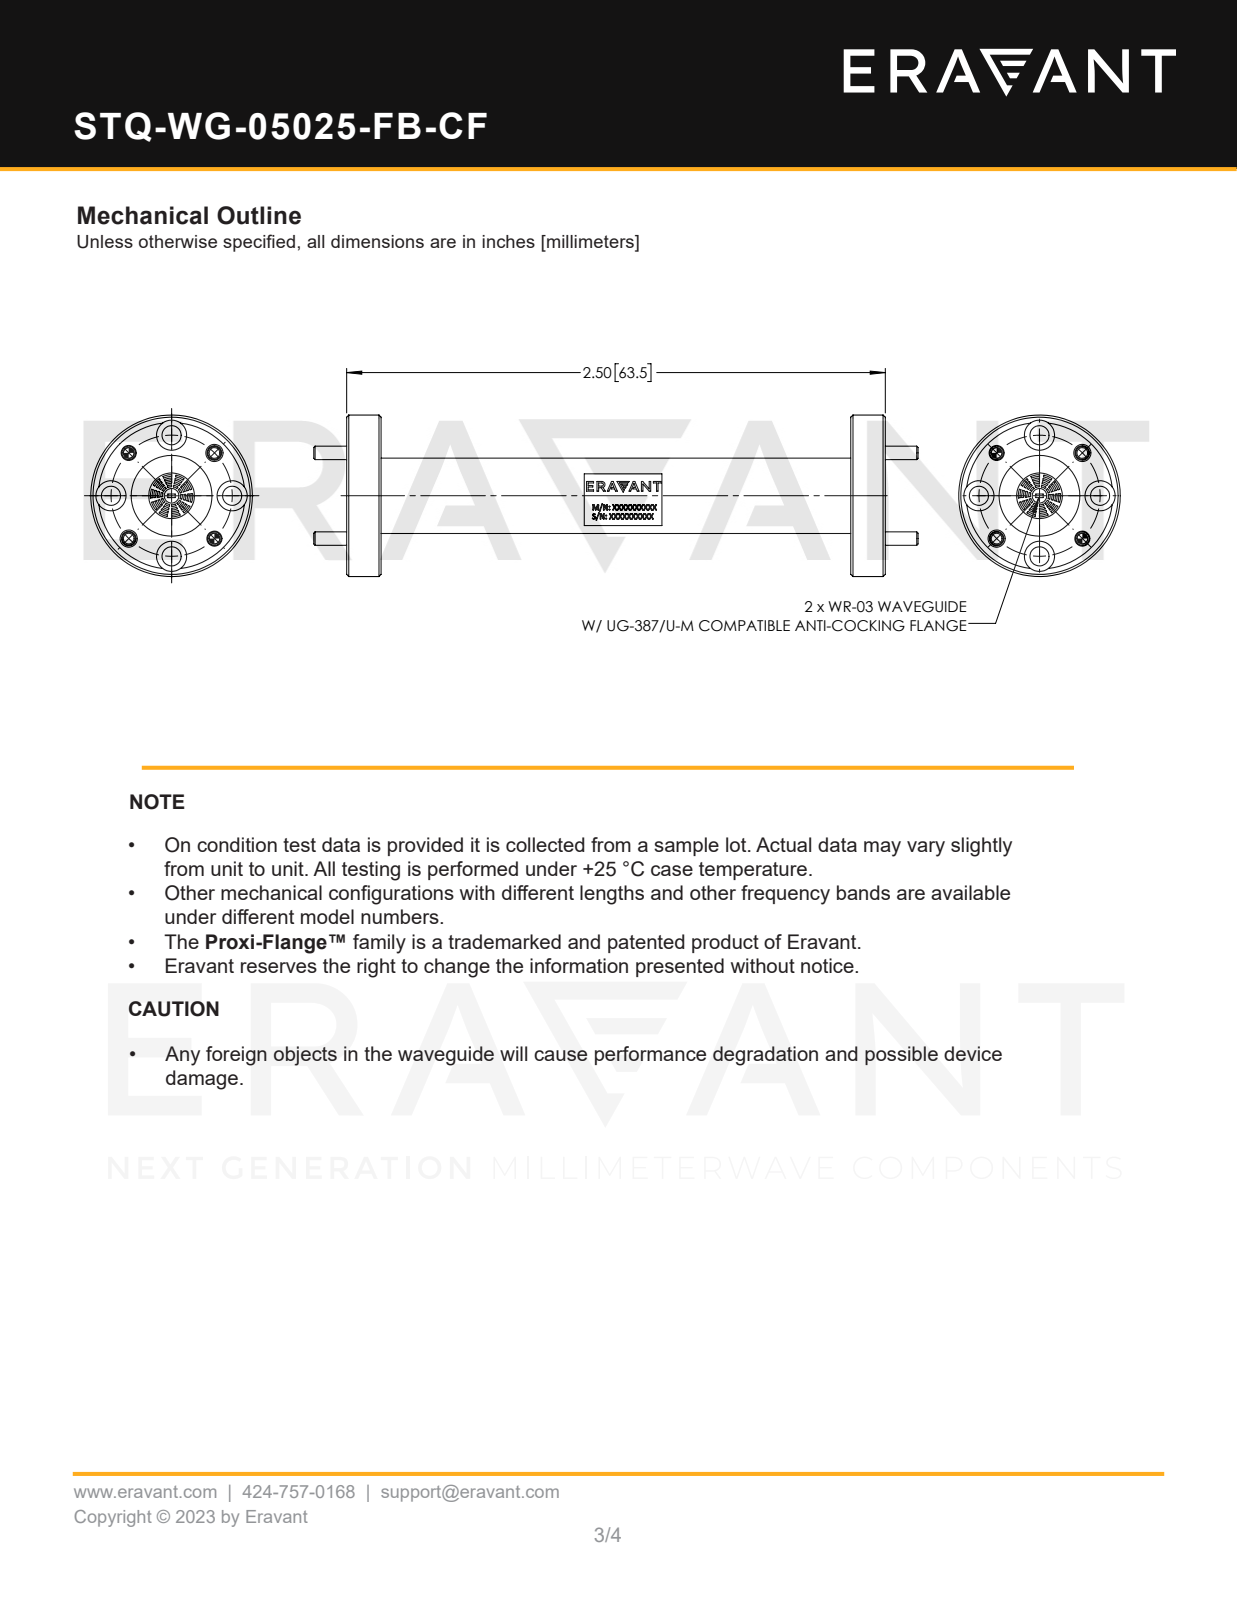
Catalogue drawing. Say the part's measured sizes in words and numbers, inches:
The part is named "WG-F03-A-CF, Defeatured". Its 3-D file was written by "SolidWorks 2021 (AUTOMOTIVE_DESIGN)". It is 5 solids with 148 faces: 34 planar, 74 cylindrical and 40 other. Overall it measures 2.805 by 0.75 by 0.75 inches. Its volume is 0.331 cubic inches and its surface area 5.501 square inches. Round holes: 4 of diameter 0.061, 4 of diameter 0.064, 4 of diameter 0.089, 4 of diameter 0.14, 1 of diameter 0.68. Round bosses or shafts: 4 of diameter 0.063, 1 of diameter 0.75, 1 of diameter 0.375, 1 of diameter 0.35. The main face-to-face distances are 0.14, 2.32, 2.18, 2.46, 2.48, 0.02, 0.16, 2.34, 2.5, 2.48. The hole center spacings are 0.215, 0.398, 0.281, 0.519, 0.52, 0.281, 0.562, 0.563.
